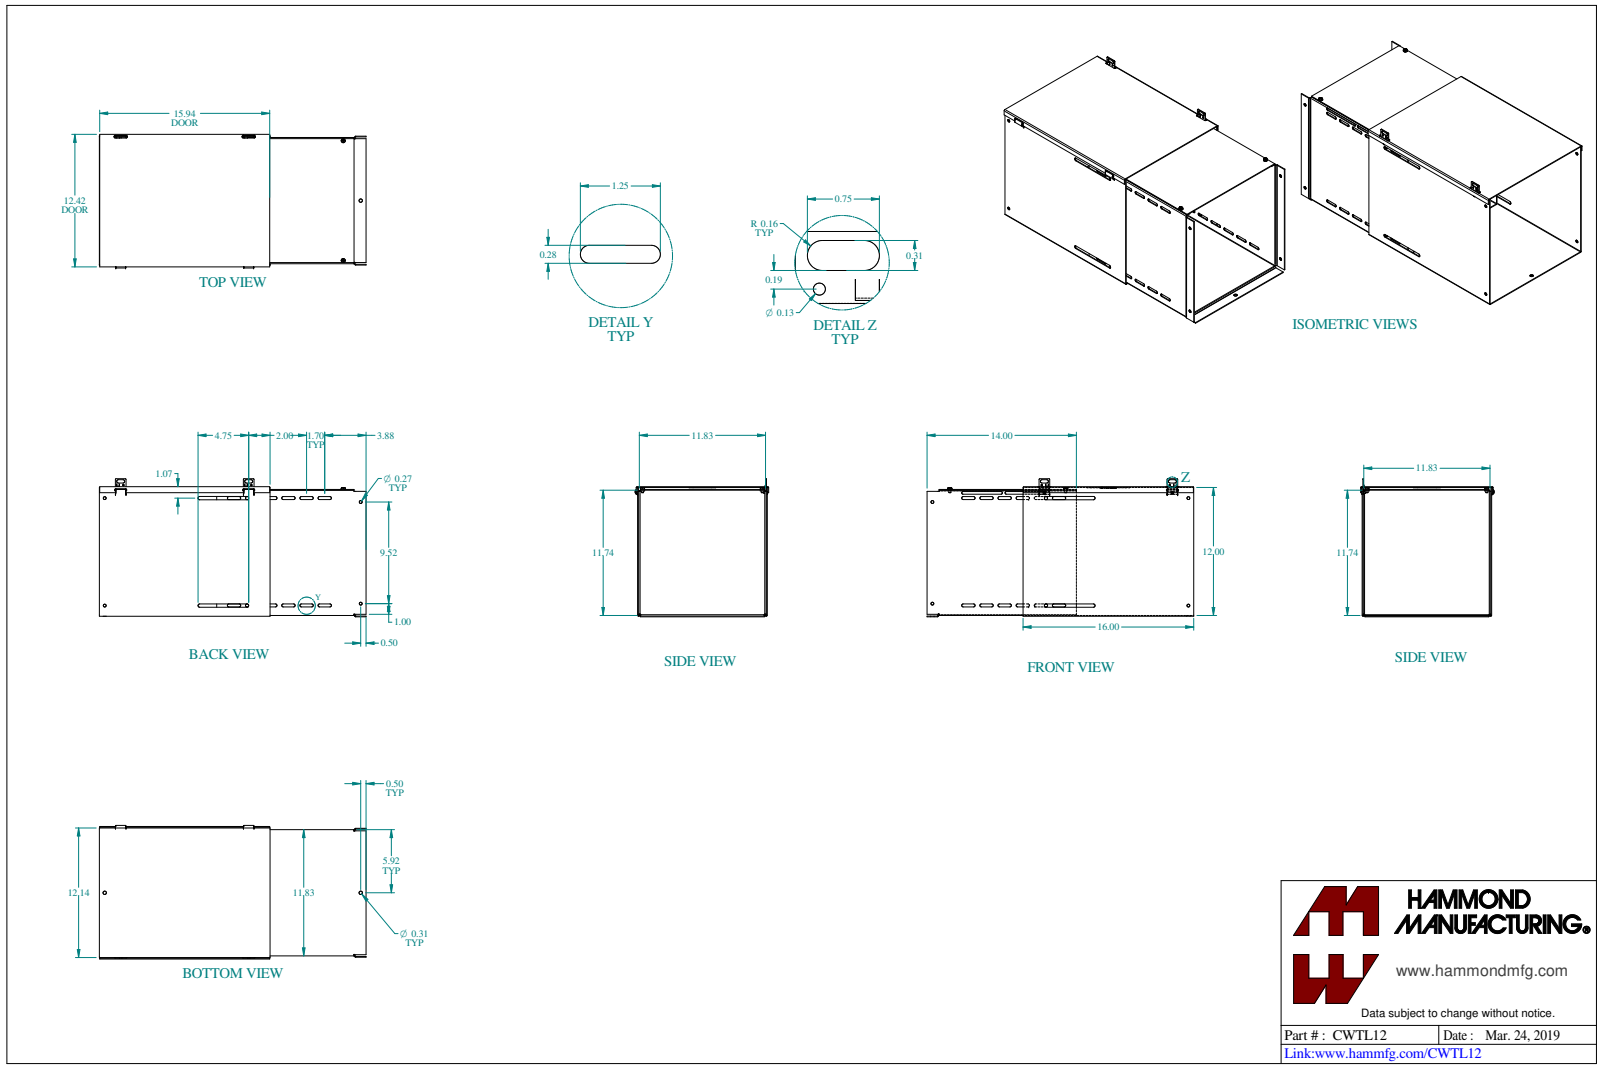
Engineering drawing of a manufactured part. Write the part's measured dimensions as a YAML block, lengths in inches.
part_name: "CWTL12"
step_written_by: "SolidWorks 2023 (CONFIG_CONTROL_DESIGN)"
units: inches
bodies: {solids: 12, faces: 506, planar: 266, cylindrical: 192, other: 48}
overall_size: [25, 12.946, 12.526]
volume: 102.8
surface_area: 2891
round_holes:
  - {diameter: 0.17, count: 4}
  - {diameter: 0.25, count: 4}
  - {diameter: 0.266, count: 4}
  - {diameter: 0.125, count: 2}
  - {diameter: 0.137, count: 2}
  - {diameter: 0.313, count: 2}
round_bosses_or_shafts:
  - {diameter: 0.375, count: 4}
  - {diameter: 0.19, count: 4}
  - {diameter: 0.125, count: 2}
partial_cylinders:
  - {radius: 0.141, count: 24}
  - {radius: 0.125, count: 20}
  - {radius: 0.036, count: 15}
  - {radius: 0.108, count: 15}
  - {radius: 0.156, count: 8}
  - {radius: 0.029, count: 1}
  - {radius: 0.086, count: 1}
  - {radius: 0.206, count: 1}
face_to_face_distances: [0.072, 12.072, 11.916, 0.156, 12, 12.144, 11.743, 11.815, 0.257, 0.228]
hole_center_spacings: [11.224, 0.763, 5.846, 5.846, 10.86, 10.863, 12, 12.796]
